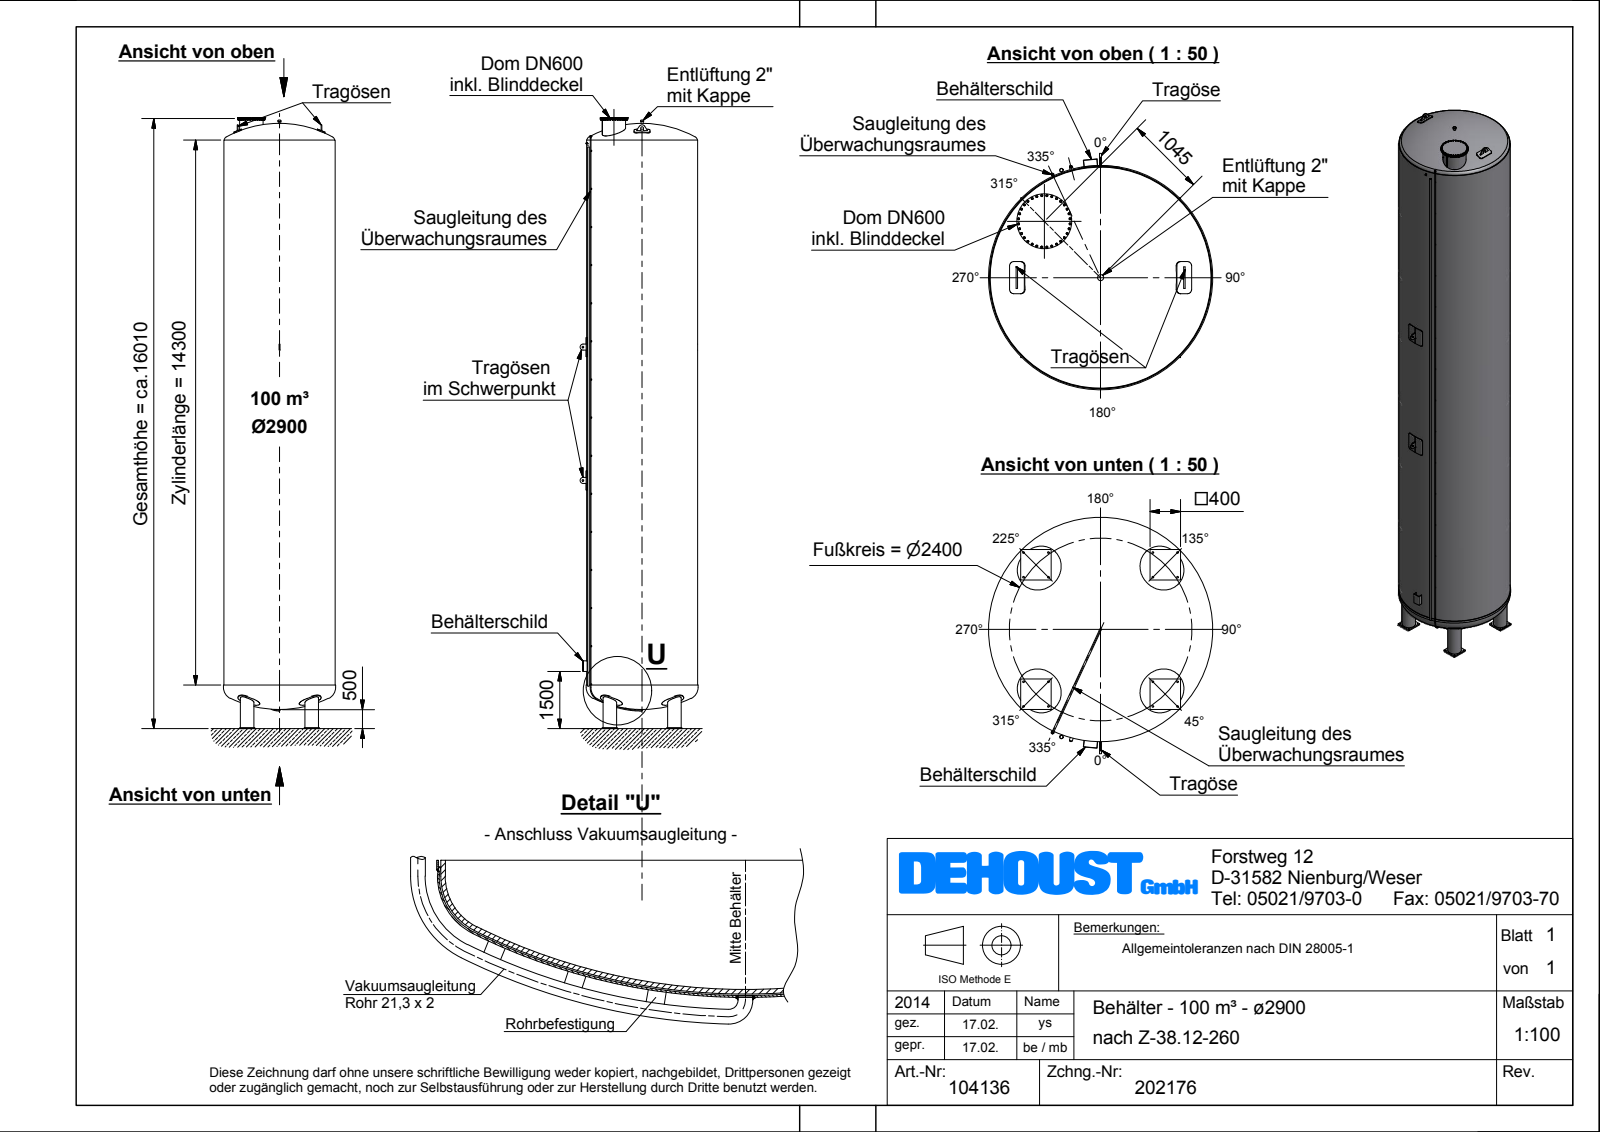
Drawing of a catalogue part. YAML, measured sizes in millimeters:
part_name: "Z-38_12-260_Beh\\S\\dlter_\\S\\x2900_100m\\S\\3_Dichte=1,0_KV"
step_written_by: "Autodesk Inventor 2012 (AUTOMOTIVE_DESIGN)"
units: millimeters
bodies: {solids: 5, faces: 220, planar: 113, cylindrical: 58, other: 49}
overall_size: [16028.62, 3101, 2942]
volume: 98820000000
surface_area: 176600000
round_holes:
  - {diameter: 230, count: 4}
  - {diameter: 336.6, count: 4}
  - {diameter: 60.3, count: 1}
  - {diameter: 598, count: 1}
round_bosses_or_shafts:
  - {diameter: 600, count: 4}
  - {diameter: 355.6, count: 4}
  - {diameter: 21.3, count: 2}
  - {diameter: 2942, count: 1}
  - {diameter: 2918, count: 1}
  - {diameter: 720, count: 1}
  - {diameter: 610, count: 1}
  - {diameter: 48.3, count: 1}
partial_cylinders:
  - {radius: 50, count: 8}
  - {radius: 56, count: 8}
  - {radius: 80, count: 2}
  - {radius: 35, count: 1}
  - {radius: 85, count: 1}
  - {radius: 1469, count: 1}
face_to_face_distances: [16, 19, 15443.23, 30, 15413.23, 16009.62, 16012.62, 16028.62, 15979.62, 15982.62]
hole_center_spacings: [1200, 1697.06, 1591.24, 2400.01, 155, 1045, 2245.01]
